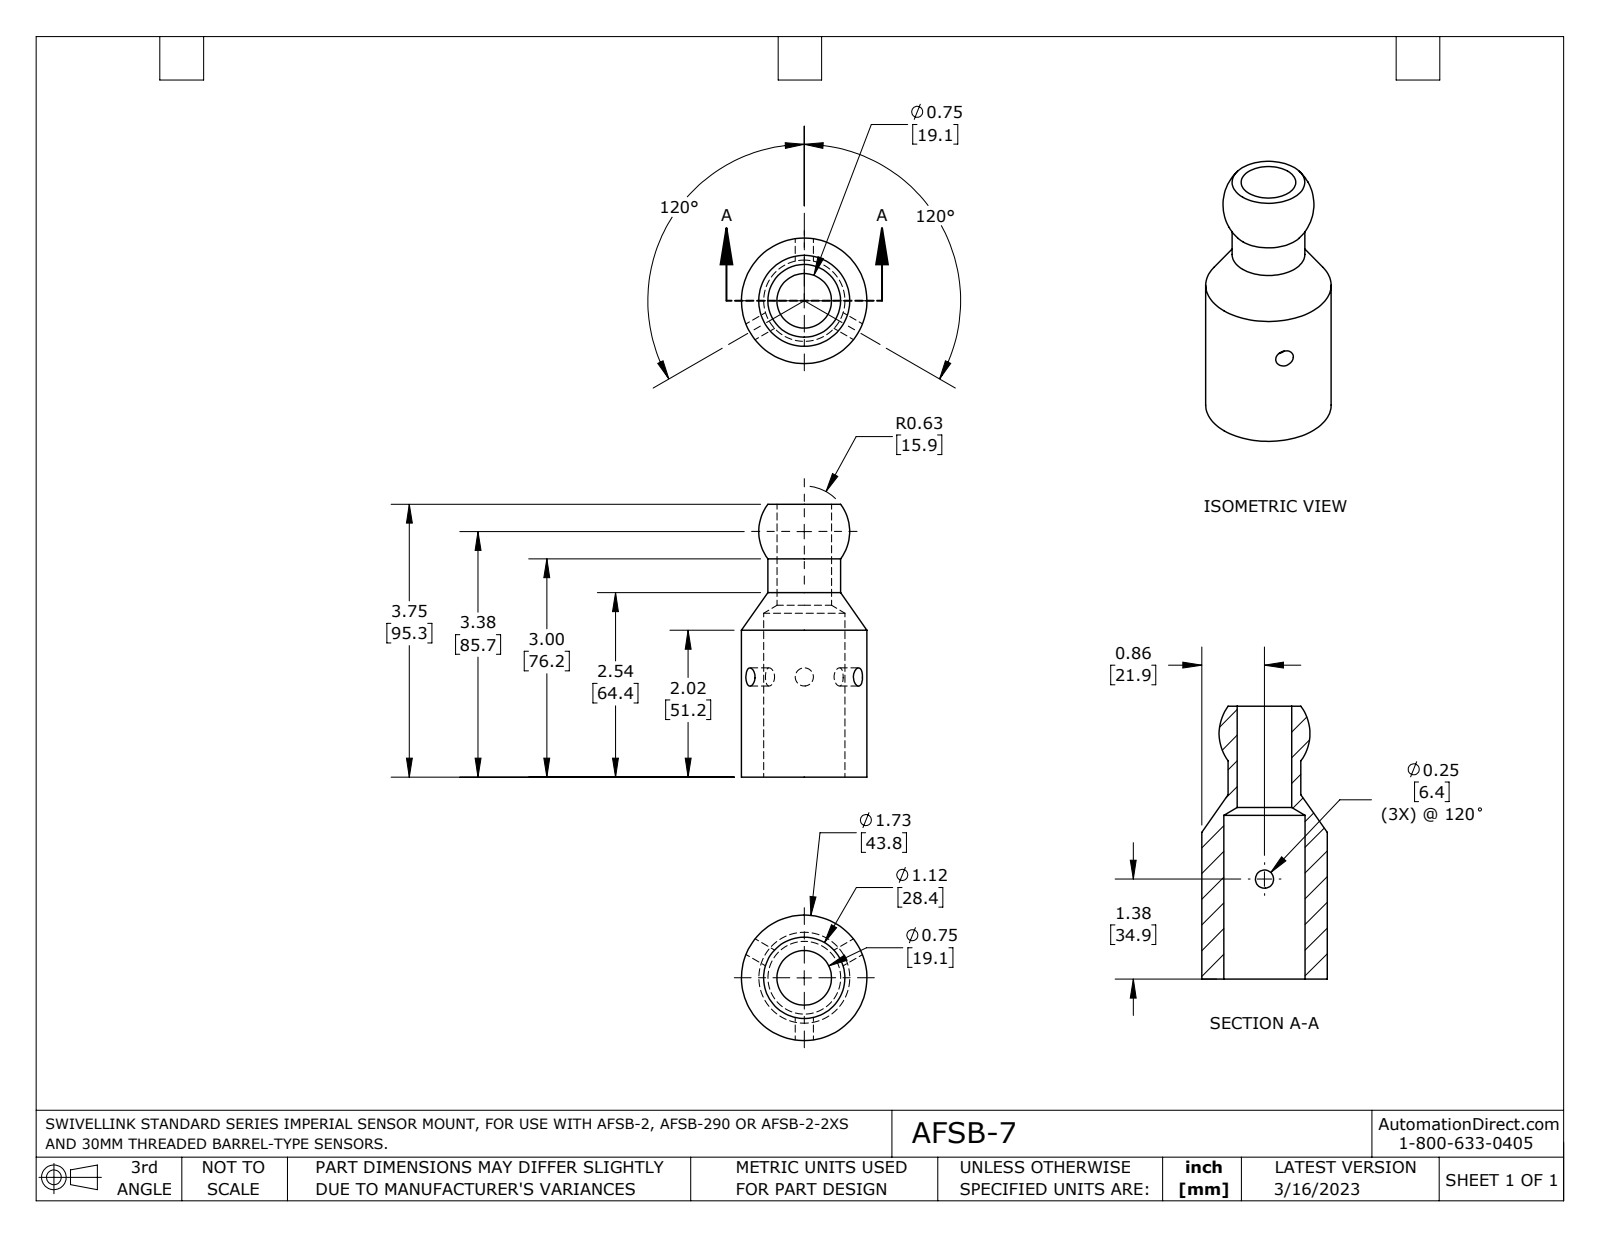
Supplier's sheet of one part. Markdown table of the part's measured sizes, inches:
| quantity | value |
| --- | --- |
| part name | AFSB-7 |
| STEP written by | SolidWorks 2021 (AUTOMOTIVE_DESIGN) |
| units | inches |
| bodies | 1 solid, 13 faces (2 planar, 7 cylindrical, 4 other) |
| overall size | 4 × 1.725 × 1.725 |
| volume | 2.699 in³ |
| surface area | 30.99 in² |
| round holes (diameter × count) | 0.25 × 3, 0.75 × 1, 1.117 × 1 |
| round bosses / shafts (diameter × count) | 1.725 × 1, 1 × 1 |
| main face-to-face distances | 3.75 |
